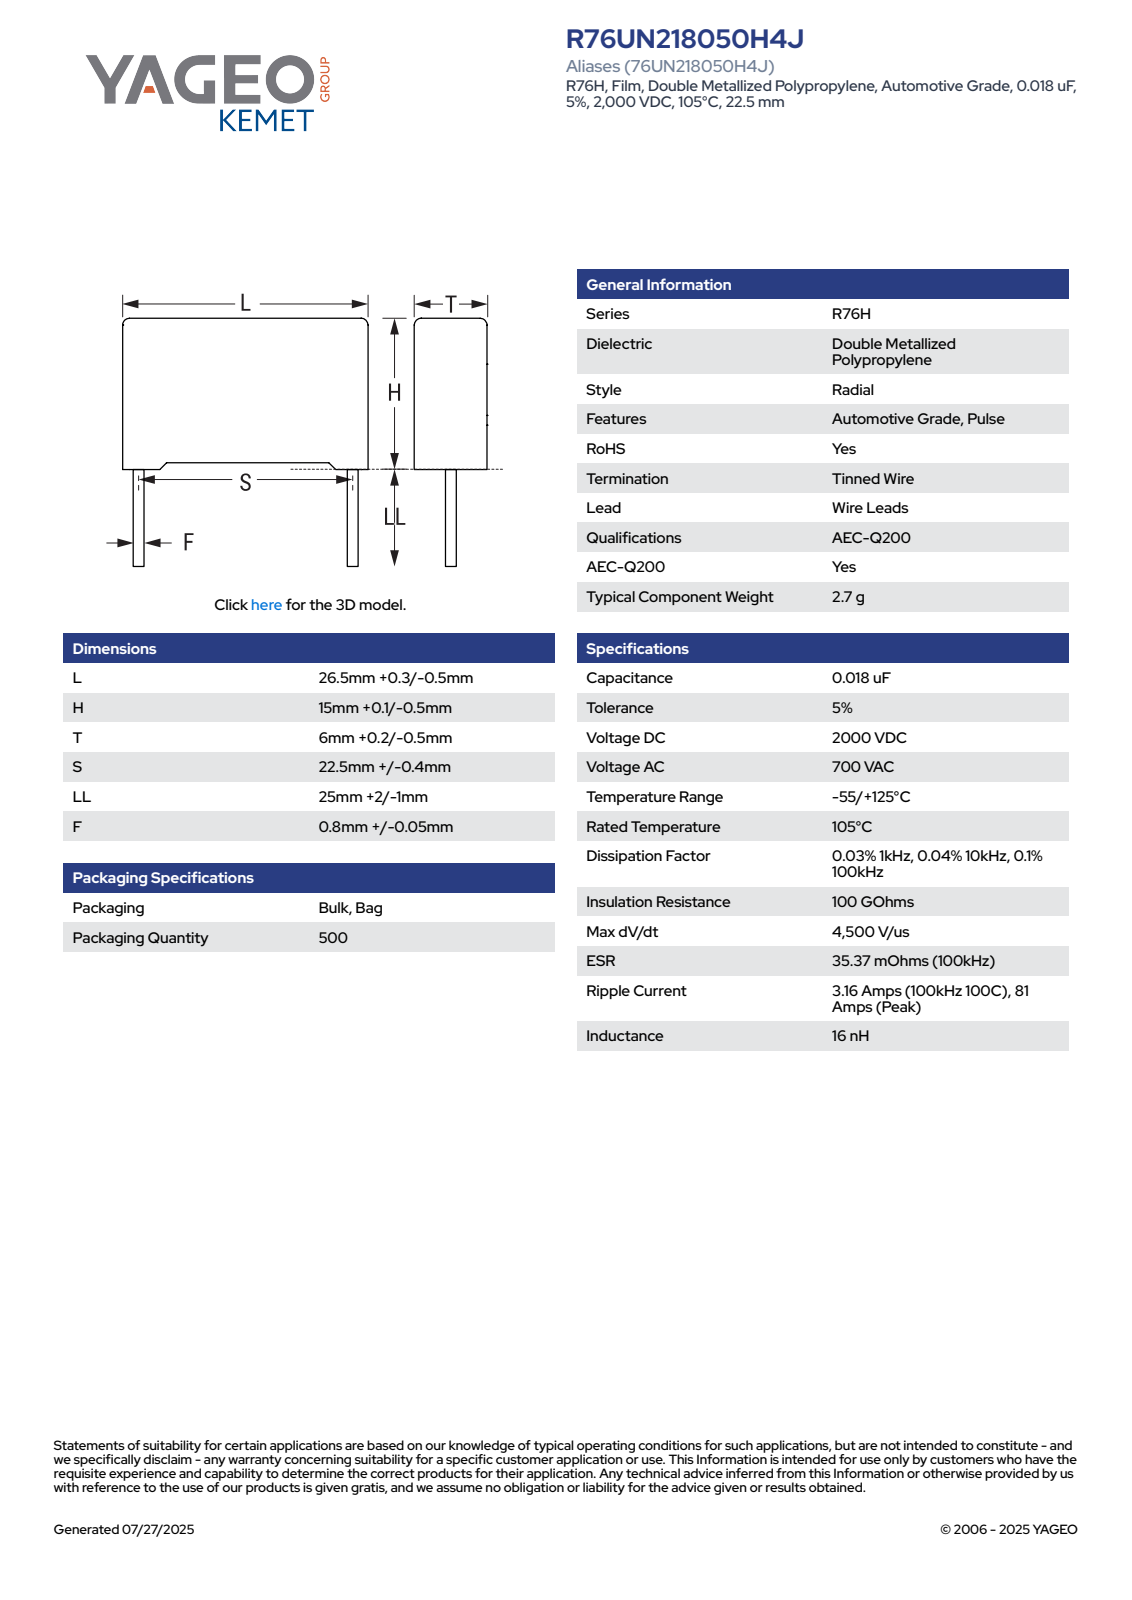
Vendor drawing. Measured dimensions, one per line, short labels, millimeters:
name: CFR_RB2R76_26.5X15X6_L26.8H15.1T6.2S22.5LL27F0.85
written by: SolidWorks 2014 (AUTOMOTIVE_DESIGN)
unit: mm
bodies: 4 solids, 85 faces (77 planar, 8 cylindrical, 0 other)
size: 42.1 × 26.8 × 6.21
volume: 2 437 mm³; area: 1 522 mm²
bosses: 2× ⌀0.85
rounds: 4× R0.5
face distances: 6.2, 14.35, 26.8, 14.58, 0.89, 0.52, 0.75, 15.1, 5.31, 4.42
